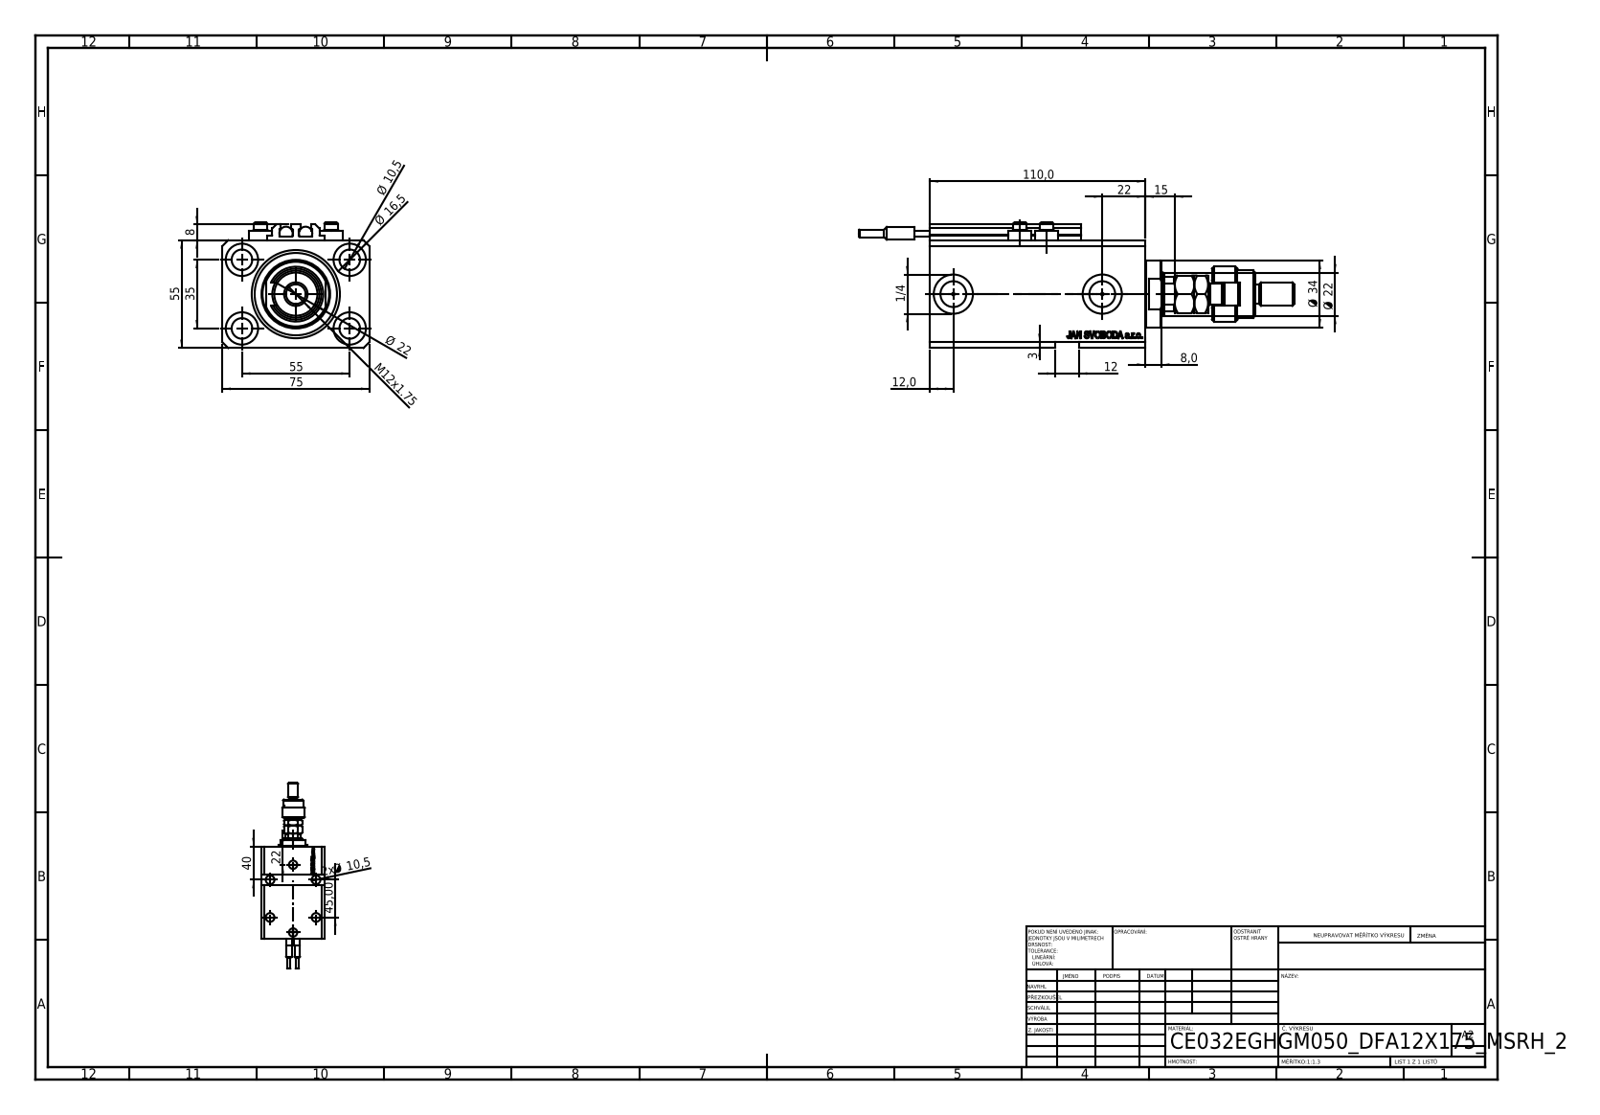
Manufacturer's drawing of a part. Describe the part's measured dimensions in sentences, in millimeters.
The part is named "MFA; V250CE_C_VCP; V250CE_E_Body; V250CE_VC_E (+3 more)". Its 3-D file was written by "SolidWorks 2019 (CONFIG_CONTROL_DESIGN)". It is 12 solids with 1221 faces: 574 planar, 171 cylindrical and 476 other. Overall it measures 222 by 75 by 64 millimeters. Its volume is 402 791 cubic millimeters and its surface area 105 514 square millimeters. Round holes: 9 of diameter 10.5, 4 of diameter 1.25, 4 of diameter 4, 4 of diameter 16.5, 2 of diameter 10, 2 of diameter 13.16, 2 of diameter 20, 1 of diameter 22, 1 of diameter 32, 1 of diameter 45. Round bosses or shafts: 4 of diameter 11.6, 4 of diameter 7, 2 of diameter 6.8, 2 of diameter 6.5, 2 of diameter 4, 1 of diameter 34, 1 of diameter 28, 1 of diameter 24. Partial cylindrical surfaces (rounded edges, fillets, slot ends): 10 of radius 0.2, 1 of radius 9.75, 1 of radius 10.5. The main face-to-face distances are 55, 75, 15, 3, 110, 57, 95, 9.9, 8, 19. The hole center spacings are 32.6, 32.87, 55, 68.74, 13.6, 14.09, 23.05, 25.81.
